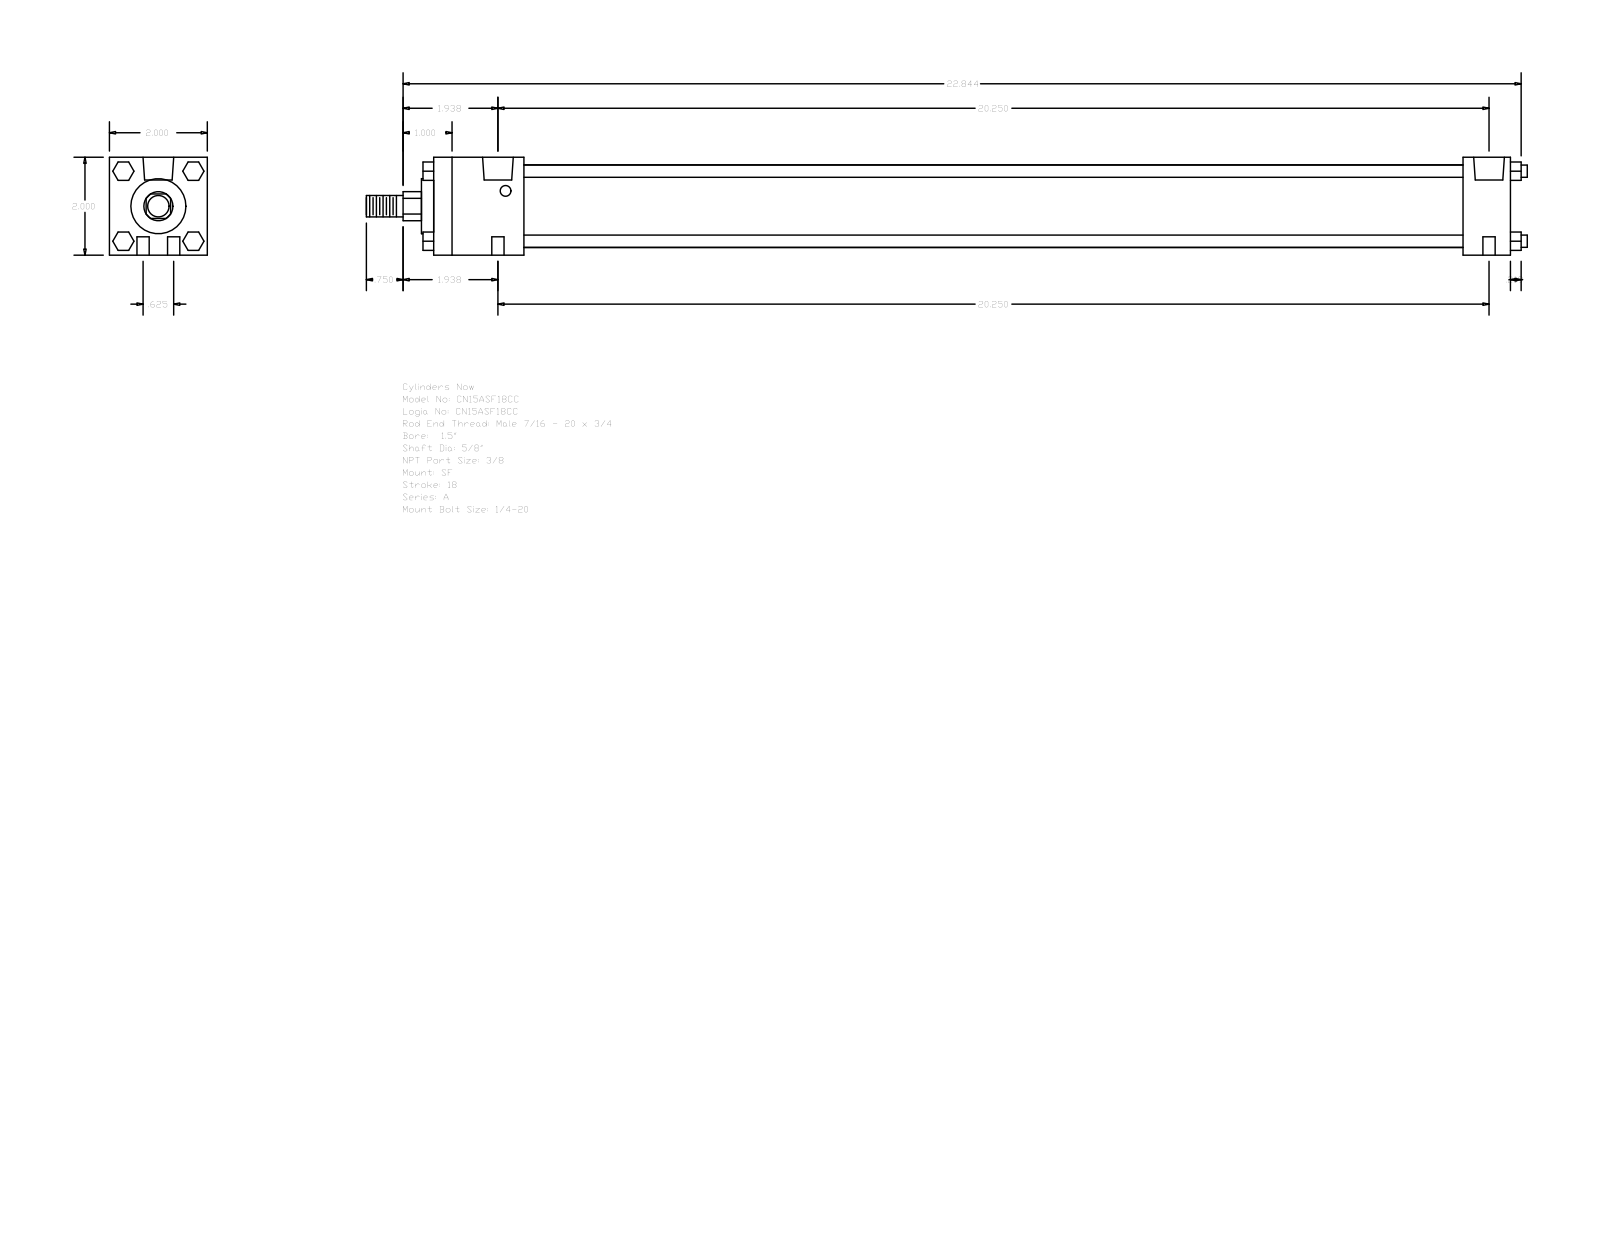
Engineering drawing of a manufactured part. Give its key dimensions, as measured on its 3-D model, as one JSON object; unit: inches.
{"part_name": "A_SF__0150_0.625", "step_written_by": "GSSL Pune (CONFIG_CONTROL_DESIGN)", "units": "inches", "bodies": {"solids": 0, "faces": 124, "planar": 94, "cylindrical": 30, "other": 0}, "overall_size": [23.719, 2, 2], "round_holes": [[0.25, 4], [0.219, 2], [0.627, 2]], "round_bosses_or_shafts": [[0.25, 4], [1.69, 1], [1.125, 1], [0.625, 1], [0.437, 1]], "partial_cylinders_radius": [[0.297, 1]], "face_to_face_distances": [2, 22, 1.844, 21.031, 19.187, 20.156, 0.969, 0.25, 0.375, 2.094], "hole_center_spacings": [0.313, 20.252, 20.25, 0.625, 20.26, 19.937]}
